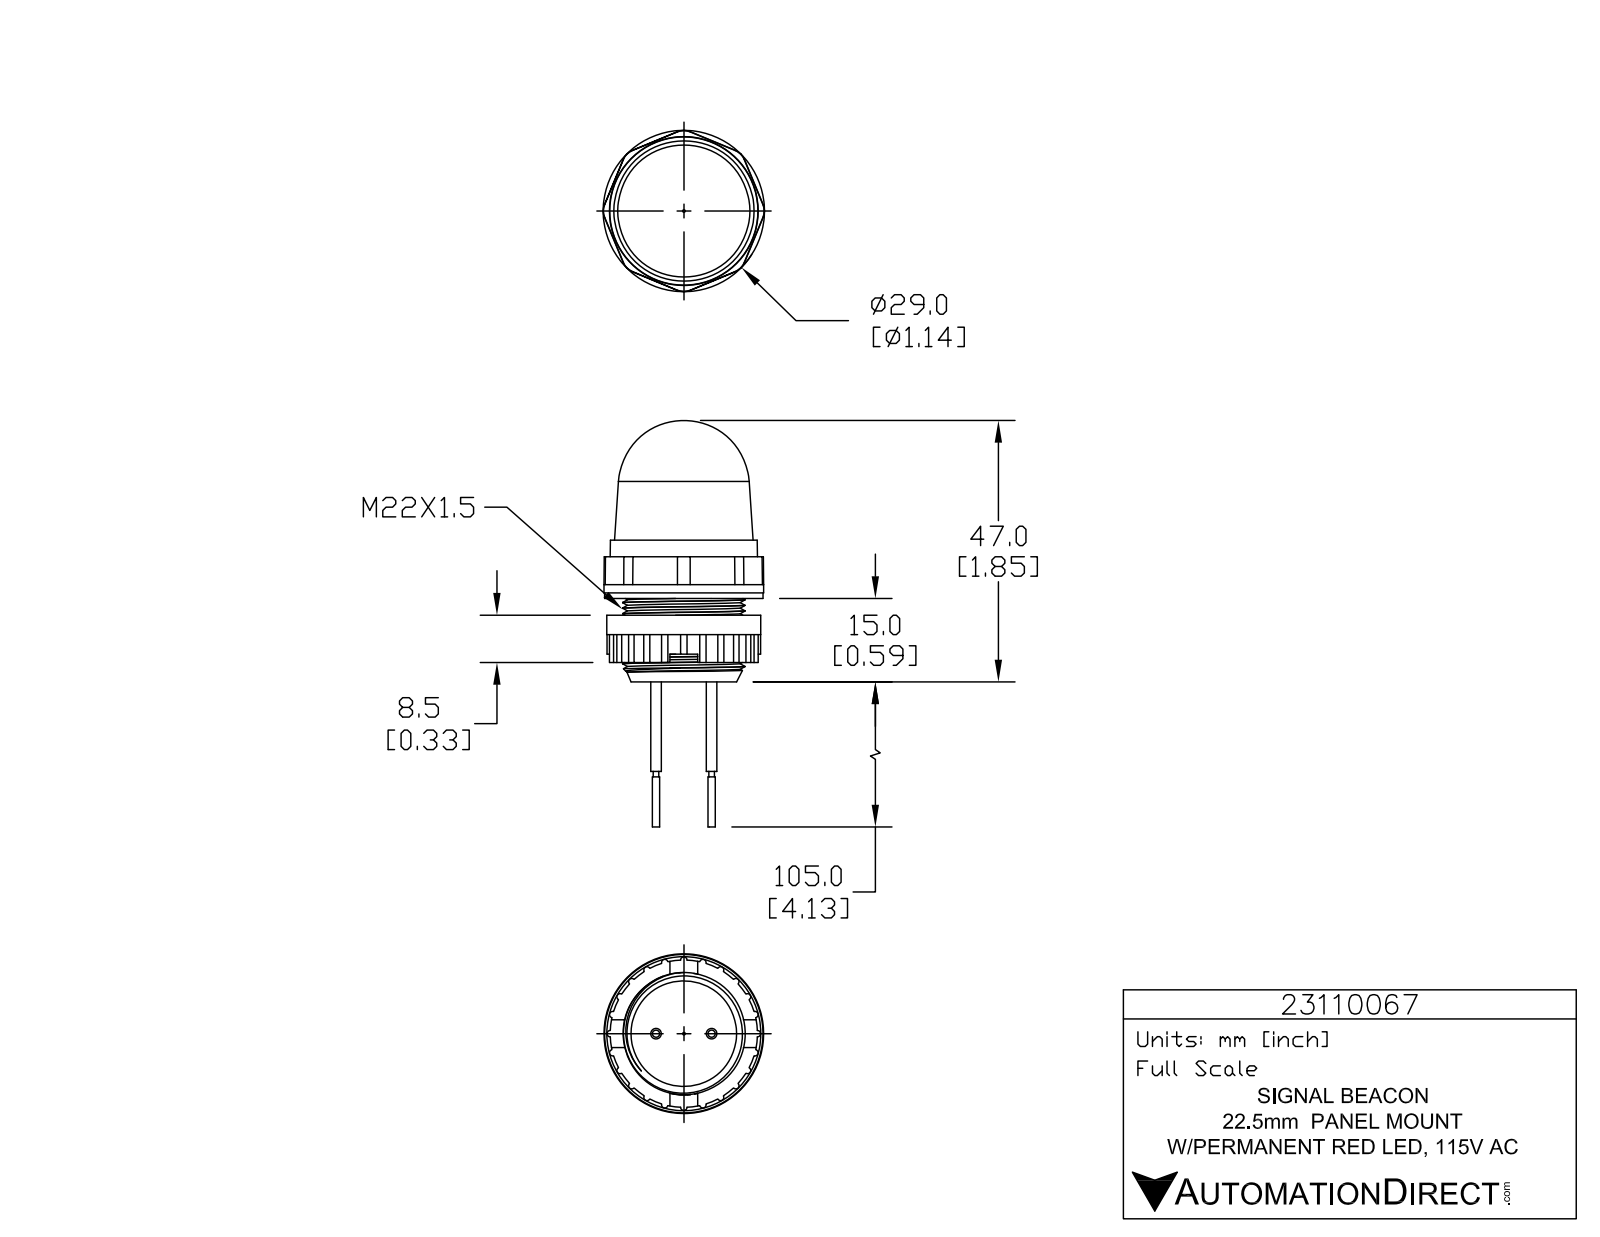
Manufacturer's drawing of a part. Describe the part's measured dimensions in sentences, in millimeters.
The part is named "23110067". Its 3-D file was written by "SolidWorks 2017 (AUTOMOTIVE_DESIGN)". It is 1 solid with 934 faces: 568 planar, 269 cylindrical and 97 other. Overall it measures 71.6 by 28.7 by 28.7 millimeters. Its volume is 20 570 cubic millimeters and its surface area 7 845 square millimeters. Round holes: 3 of diameter 0.5. Round bosses or shafts: 3 of diameter 2.9, 3 of diameter 0.7, 2 of diameter 1.9, 2 of diameter 1.3, 2 of diameter 1, 1 of diameter 28.7, 1 of diameter 28.5, 1 of diameter 27.7. Partial cylindrical surfaces (rounded edges, fillets, slot ends): 24 of radius 0.6, 8 of radius 3, 6 of radius 0.1, 6 of radius 0.1, 6 of radius 0.1, 6 of radius 1.7, 3 of radius 0.1, 3 of radius 0.2. The main face-to-face distances are 14, 3, 11, 2.5, 8.5, 11.5, 12.5, 10.5, 7.5, 5.
